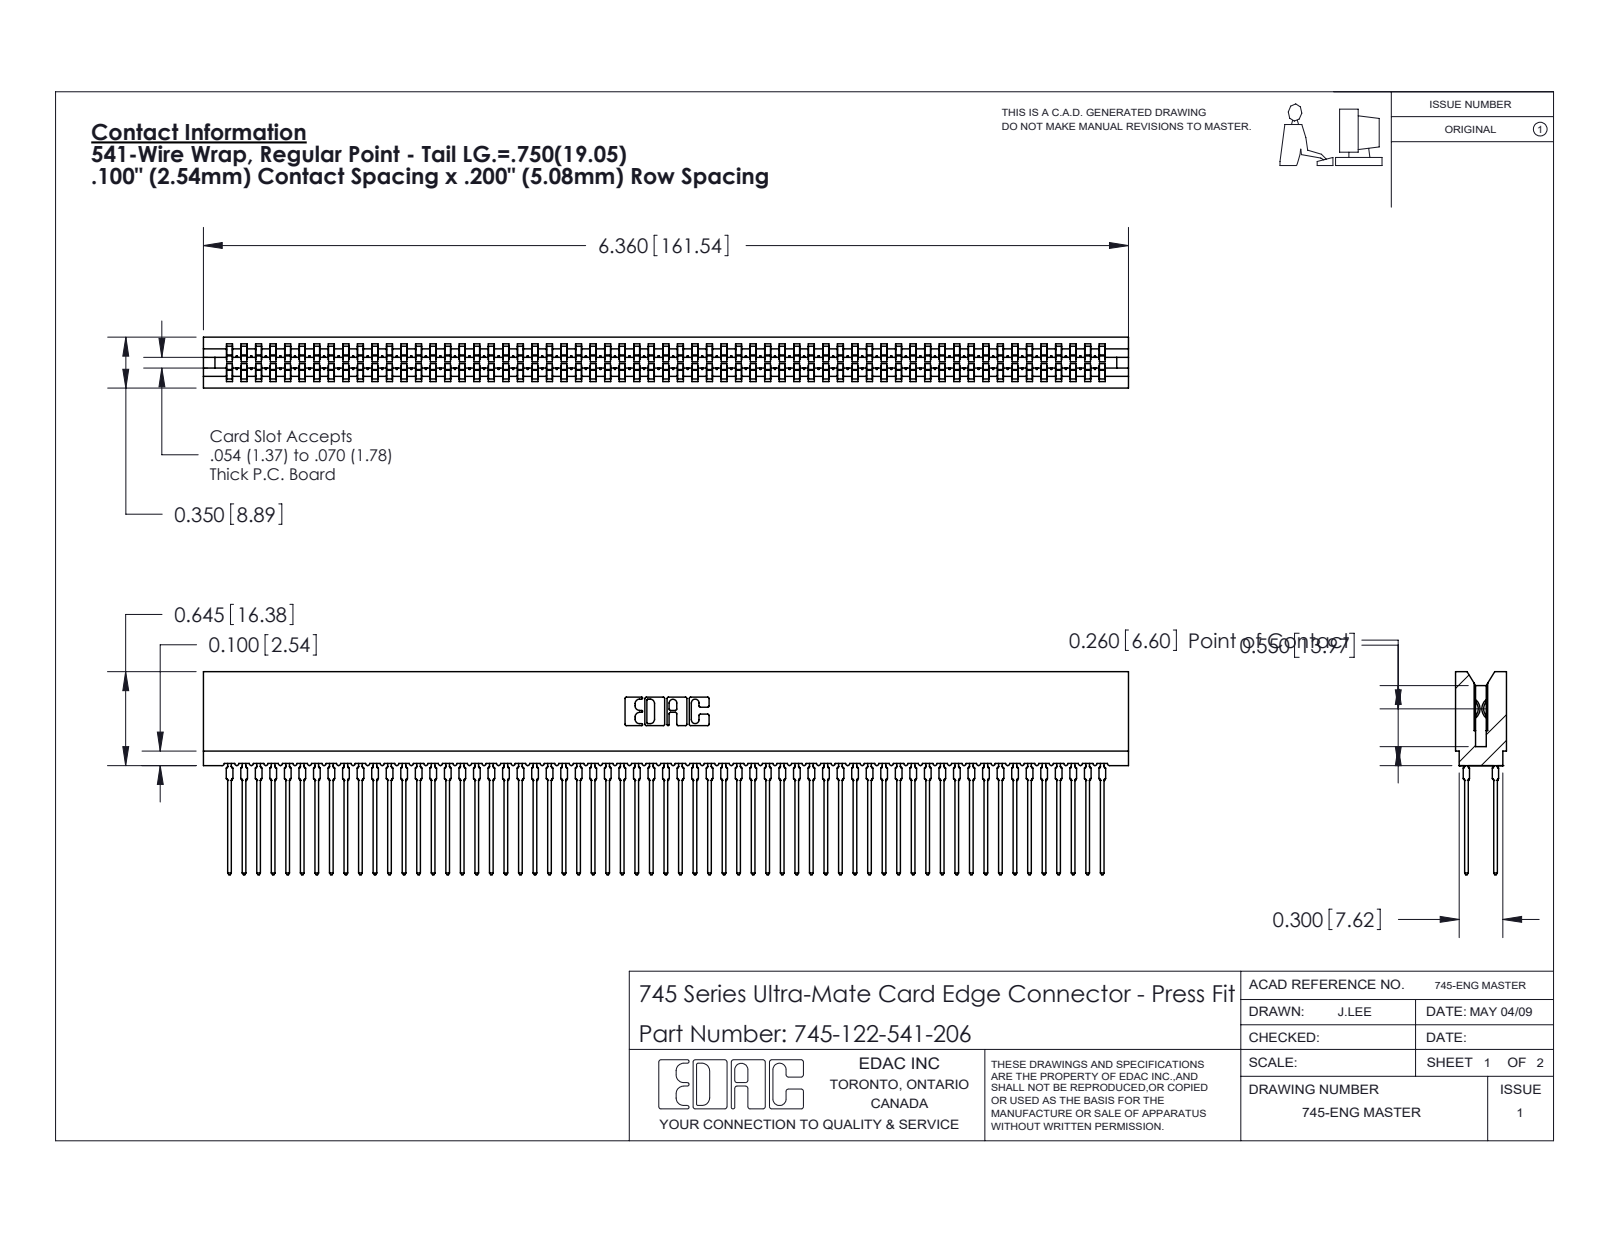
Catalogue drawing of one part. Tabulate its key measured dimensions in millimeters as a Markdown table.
| quantity | value |
| --- | --- |
| part name | 745-122-541-206; 745-292-001_541; 745 Part_Insulator Option - 06 |
| STEP written by | SolidWorks 2020 (CONFIG_CONTROL_DESIGN) |
| units | millimeters |
| bodies | 123 solids, 11015 faces (5668 planar, 2175 cylindrical, 3172 other) |
| overall size | 161.5 × 35.5 × 8.9 |
| volume | 15 000 mm³ |
| surface area | 33 400 mm² |
| partial cylindrical surfaces (radius × count) | 0.5 × 244, 0.4 × 122, 0.3 × 22, 0.1 × 8, 0.3 × 8, 0.2 × 6, 0.8 × 6, 0.7 × 3 |
| main face-to-face distances | 1.6, 7.3, 5.1, 8.9, 2.2, 6.7, 0.6, 1.1, 7.7, 0.5 |
